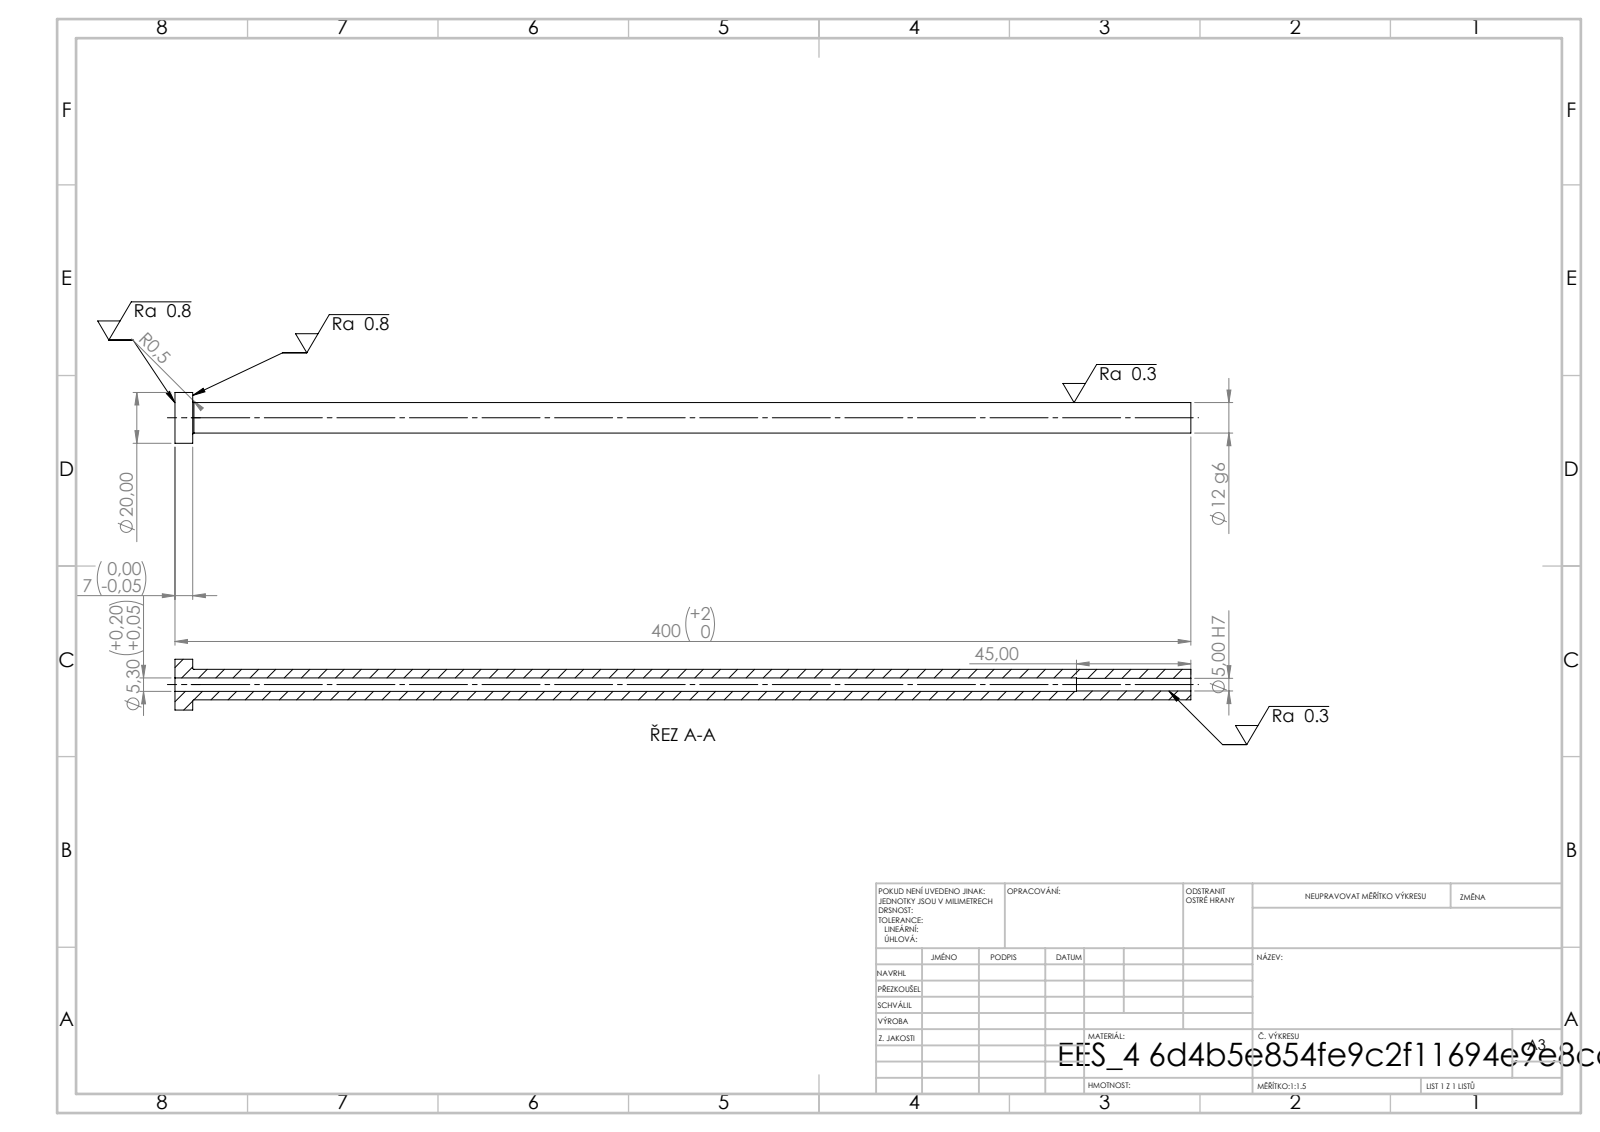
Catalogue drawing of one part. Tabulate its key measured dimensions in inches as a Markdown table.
| quantity | value |
| --- | --- |
| STEP written by | SolidWorks 2019 (CONFIG_CONTROL_DESIGN) |
| units | inches |
| bodies | 1 solid, 14 faces (4 planar, 8 cylindrical, 2 other) |
| overall size | 15.748 × 0.787 × 0.787 |
| volume | 2.315 in³ |
| surface area | 34.8 in² |
| round holes (diameter × count) | 0.197 × 1, 0.209 × 1 |
| round bosses / shafts (diameter × count) | 0.787 × 1, 0.472 × 1 |
| main face-to-face distances | 0.276, 15.748, 15.472, 13.976, 13.701, 1.772 |
